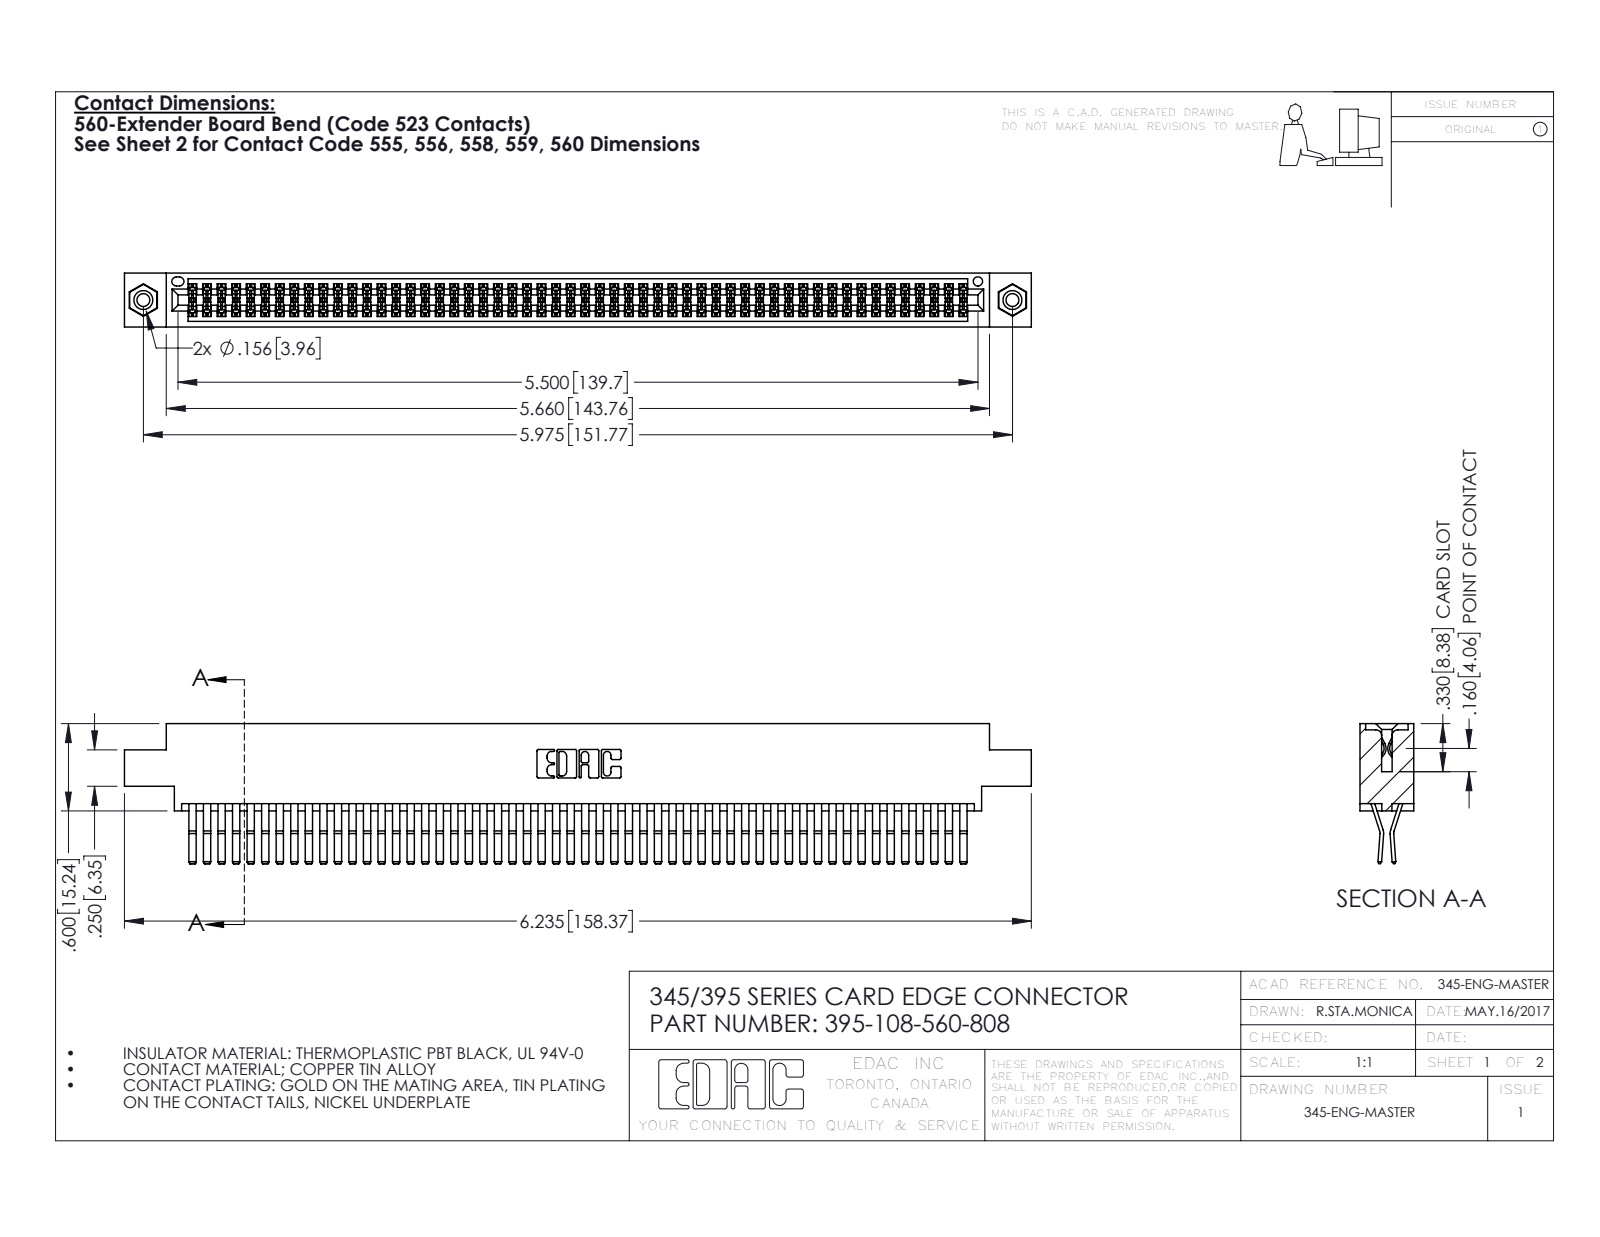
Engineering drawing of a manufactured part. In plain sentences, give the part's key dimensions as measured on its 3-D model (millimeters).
The part is named "395-108-560-808; 345-292-001_560 Tail; 345 Part_0.170 Offset - 0.156 Dia-TI; 345-250-001_345-250-003-102". Its 3-D file was written by "SolidWorks 2016 (CONFIG_CONTROL_DESIGN)". It is 111 solids with 5806 faces: 3680 planar, 2110 cylindrical and 16 other. Overall it measures 158.4 by 24.4 by 9.4 millimeters. Its volume is 16 100 cubic millimeters and its surface area 25 990 square millimeters. Round holes: 2 of diameter 2.3, 2 of diameter 3.2, 2 of diameter 4, 1 of diameter 1.6. Round bosses or shafts: 2 of diameter 3.9. Partial cylindrical surfaces (rounded edges, fillets, slot ends): 162 of radius 0.2, 22 of radius 0.3, 6 of radius 0.2, 6 of radius 0.8, 3 of radius 0.7, 2 of radius 0.3, 2 of radius 0.4, 2 of radius 0.5. The main face-to-face distances are 0.6, 1.8, 7.6, 9.4, 5.1, 2.5, 6.9, 5.7, 4.4, 3.8. The hole center spacings are 6.9, 145.8, 151.8.
